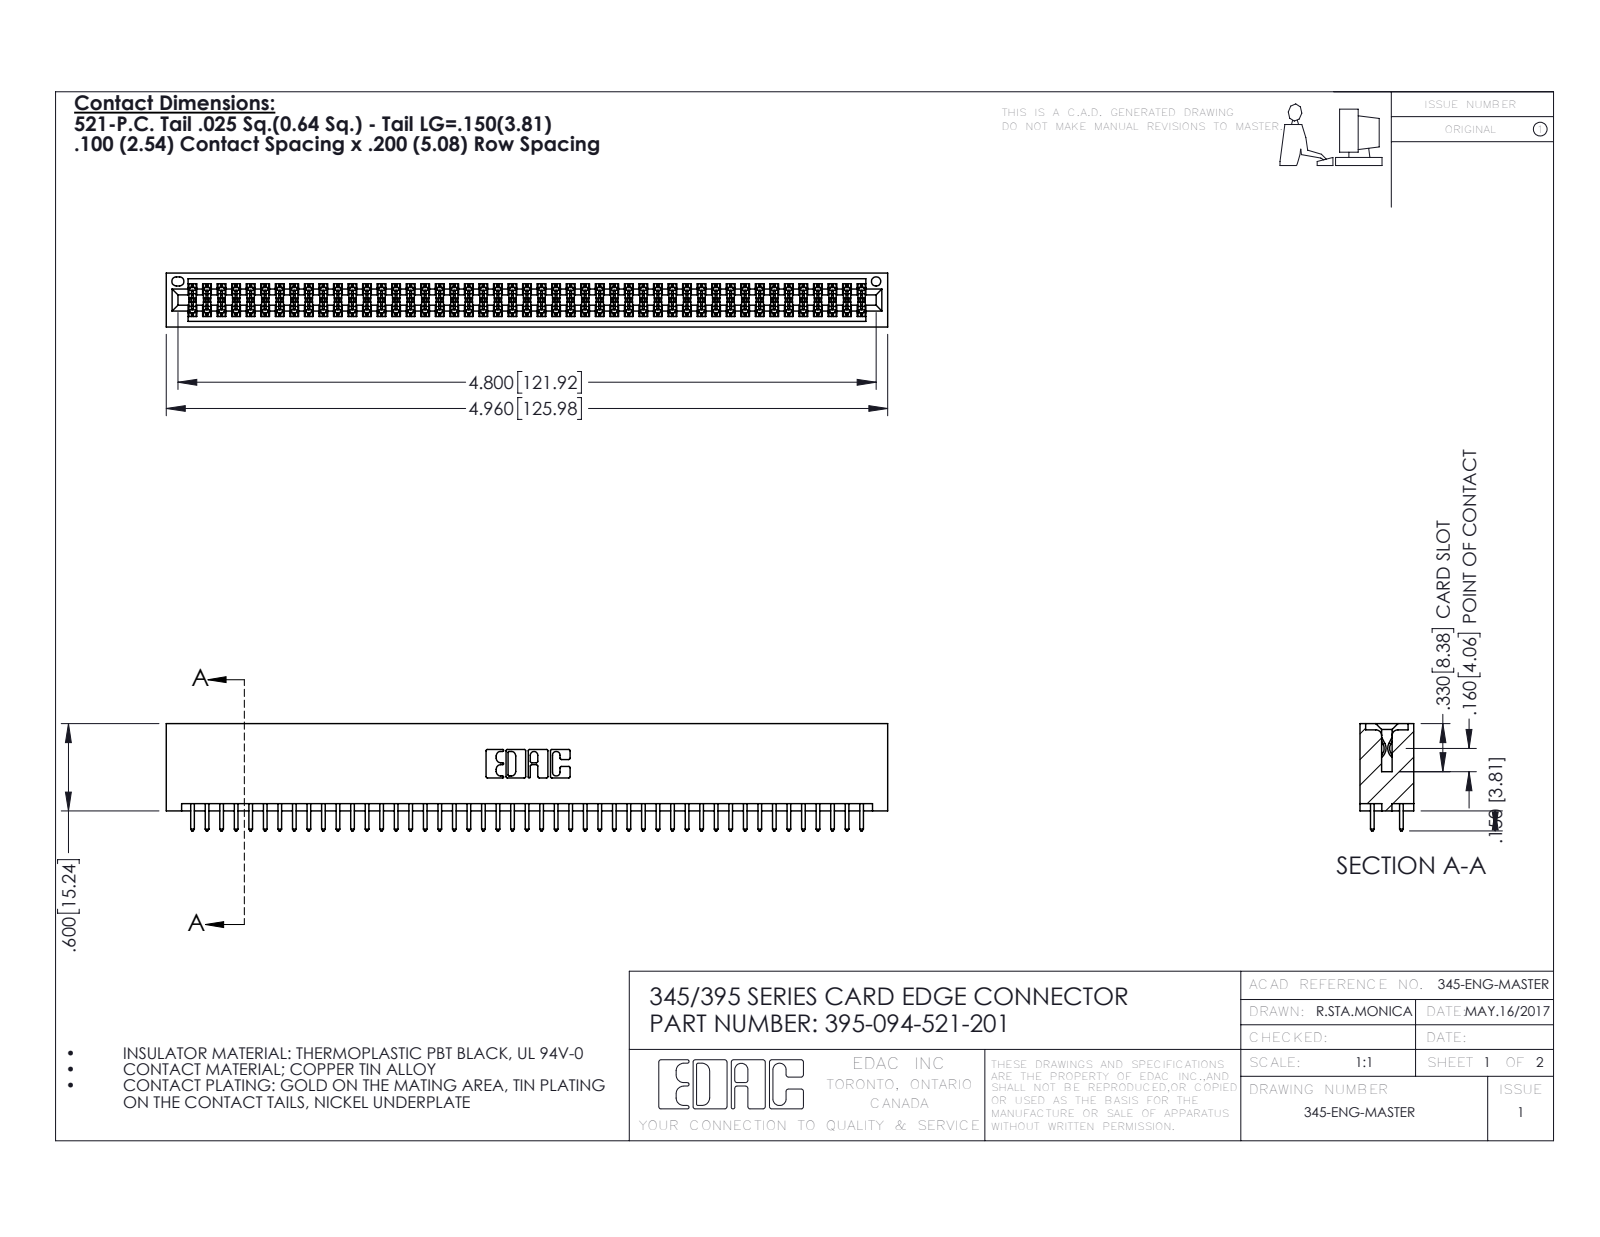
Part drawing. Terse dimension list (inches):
name: 345 Part_No Mounting Lugs; 345-292-001_345-293-121; 395-094-521-201
written by: SolidWorks 2016 (CONFIG_CONTROL_DESIGN)
unit: in
bodies: 95 solids, 4818 faces (3178 planar, 1640 cylindrical, 0 other)
size: 4.96 × 0.737 × 0.37
volume: 0.785 in³; area: 29.7 in²
holes: 1× ⌀0.064
rounds: 141× R0.006, 94× R0.01, 22× R0.01, 6× R0.007, 6× R0.031, 3× R0.026, 2× R0.014, 2× R0.019
face distances: 0.298, 0.072, 0.2, 0.098, 0.272, 0.025, 0.37, 0.225, 0.175, 0.149
